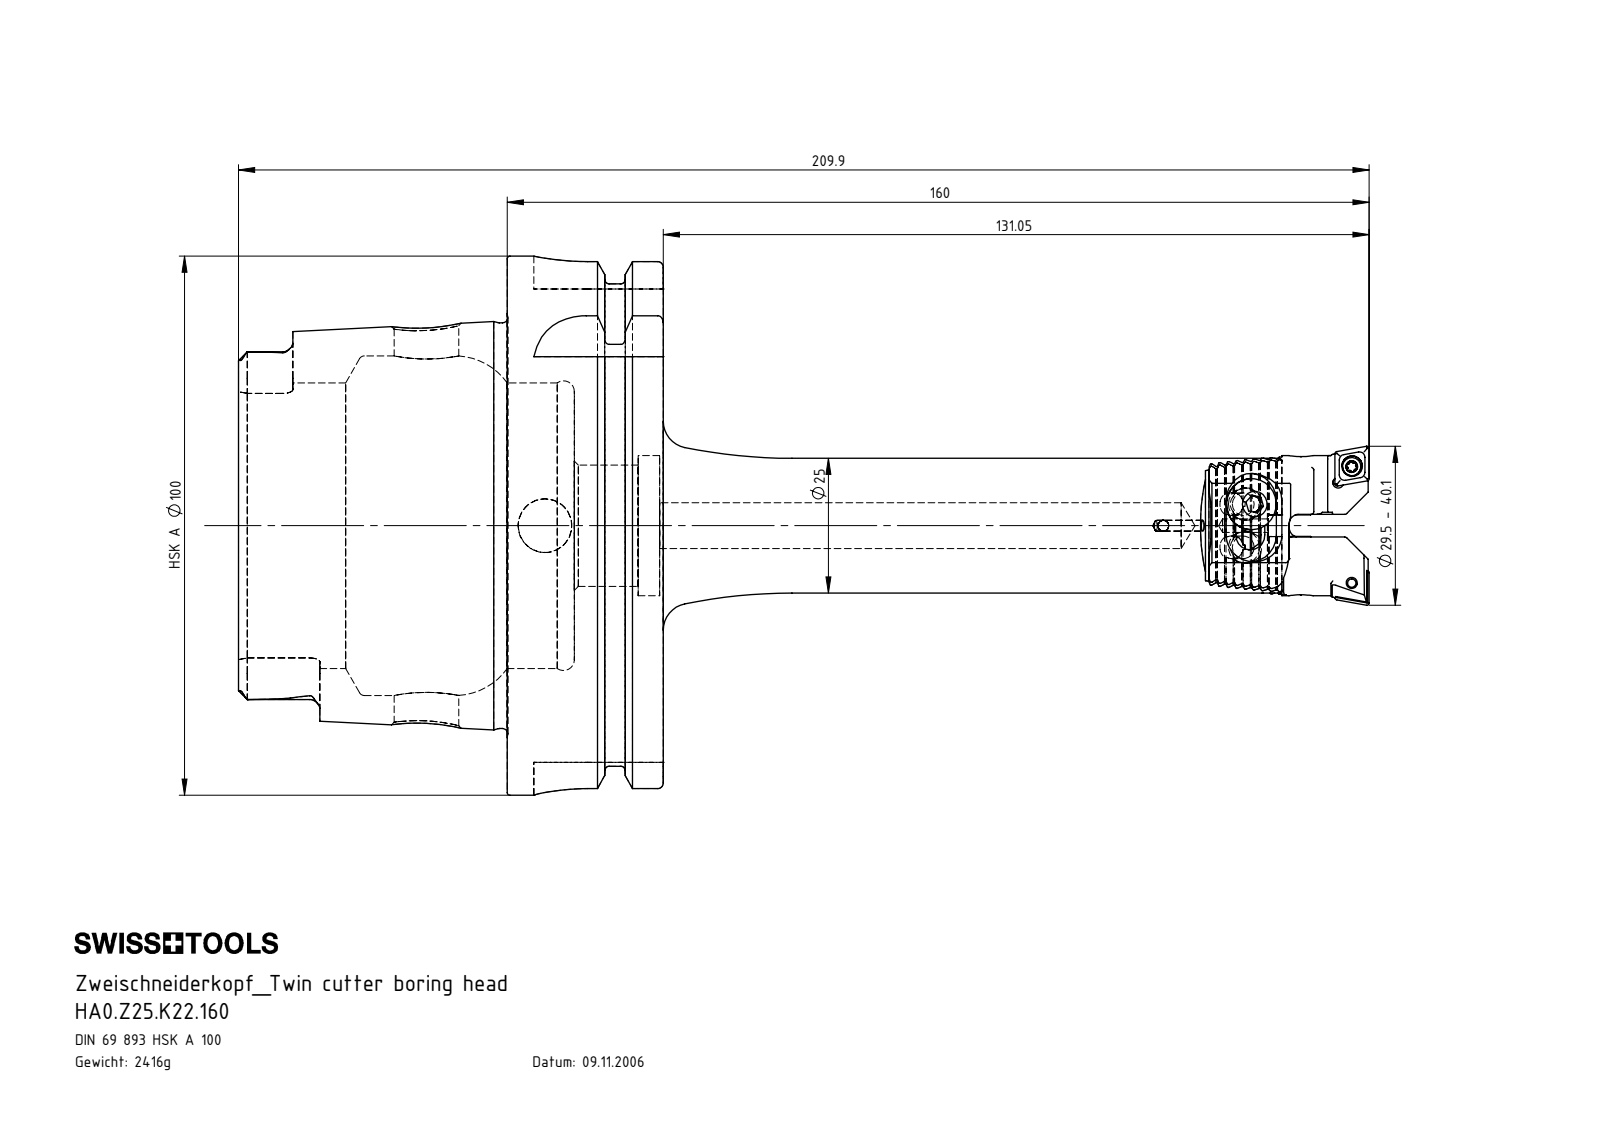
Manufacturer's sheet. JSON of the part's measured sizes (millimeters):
{"part_name": "Z25-ER1.001.012; CCMT060204; Z25-ER1.003.012_A_gespannt; HA0.Z25.K22.160 (+7 more)", "step_written_by": "SolidWorks 2022 (CONFIG_CONTROL_DESIGN)", "units": "millimeters", "bodies": {"solids": 14, "faces": 1073, "planar": 496, "cylindrical": 280, "other": 297}, "overall_size": [209.9, 100, 100], "volume_mm3": 308403, "surface_area_mm2": 67374, "round_holes": [[2, 5], [1.6, 2], [2.05, 2], [2.8, 2], [3.85, 2], [4.2, 2], [5.3, 2], [6, 2], [2.5, 1], [3.5, 1], [8.5, 1], [10, 1]], "round_bosses_or_shafts": [[9.5, 2], [9.2, 2], [5, 2], [3.4, 2], [2.5, 2], [100, 1], [91.95, 1], [75.26, 1]], "partial_cylinders_radius": [[0.12, 18], [0.5, 18], [0.12, 16], [0.21, 12], [0.36, 10], [1.9, 6], [2, 4], [2.8, 4]], "face_to_face_distances": [28.95, 12.45, 16.5, 1.43, 49.9, 62.35, 78.85, 2.86, 0.65, 78.2], "hole_center_spacings": [3.9, 4, 7, 18.02, 18.11, 20.91, 164.3, 13.52]}
